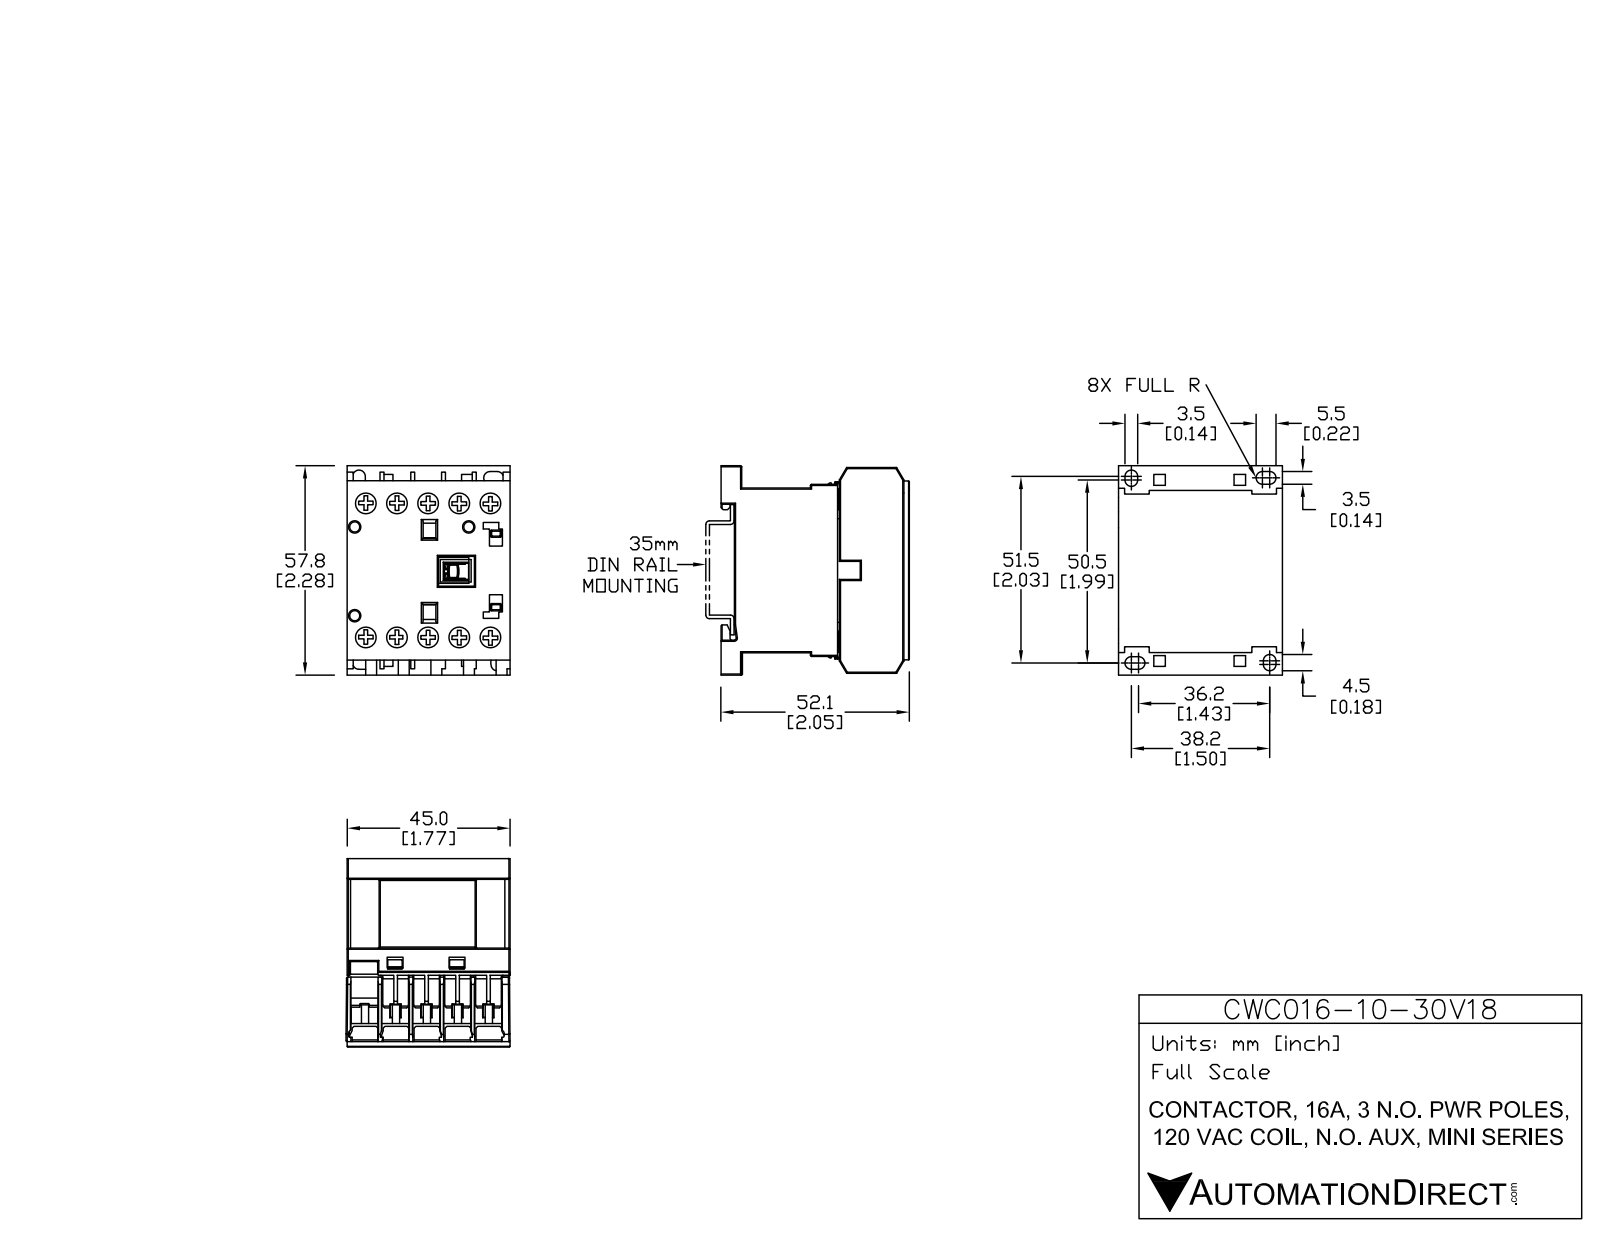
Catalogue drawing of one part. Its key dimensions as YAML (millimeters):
part_name: "CWC16-10-30V18"
step_written_by: "SolidWorks 2013 (AUTOMOTIVE_DESIGN)"
units: millimeters
bodies: {solids: 15, faces: 535, planar: 445, cylindrical: 90, other: 0}
overall_size: [58.04, 52.12, 45.75]
volume: 97133
surface_area: 30437
round_holes:
  - {diameter: 6.2, count: 10}
  - {diameter: 2.8, count: 3}
round_bosses_or_shafts:
  - {diameter: 5.9, count: 10}
partial_cylinders:
  - {radius: 0.3, count: 20}
  - {radius: 1.72, count: 6}
  - {radius: 1.73, count: 2}
  - {radius: 0.32, count: 1}
  - {radius: 0.42, count: 1}
  - {radius: 0.55, count: 1}
face_to_face_distances: [8.25, 45.5, 1.25, 16.5, 9.5, 5.5, 17.75, 5.13, 10.63, 7]
hole_center_spacings: [8.55, 37.94, 17.1, 40.72, 36.96, 25.65, 44.99, 6.91]
